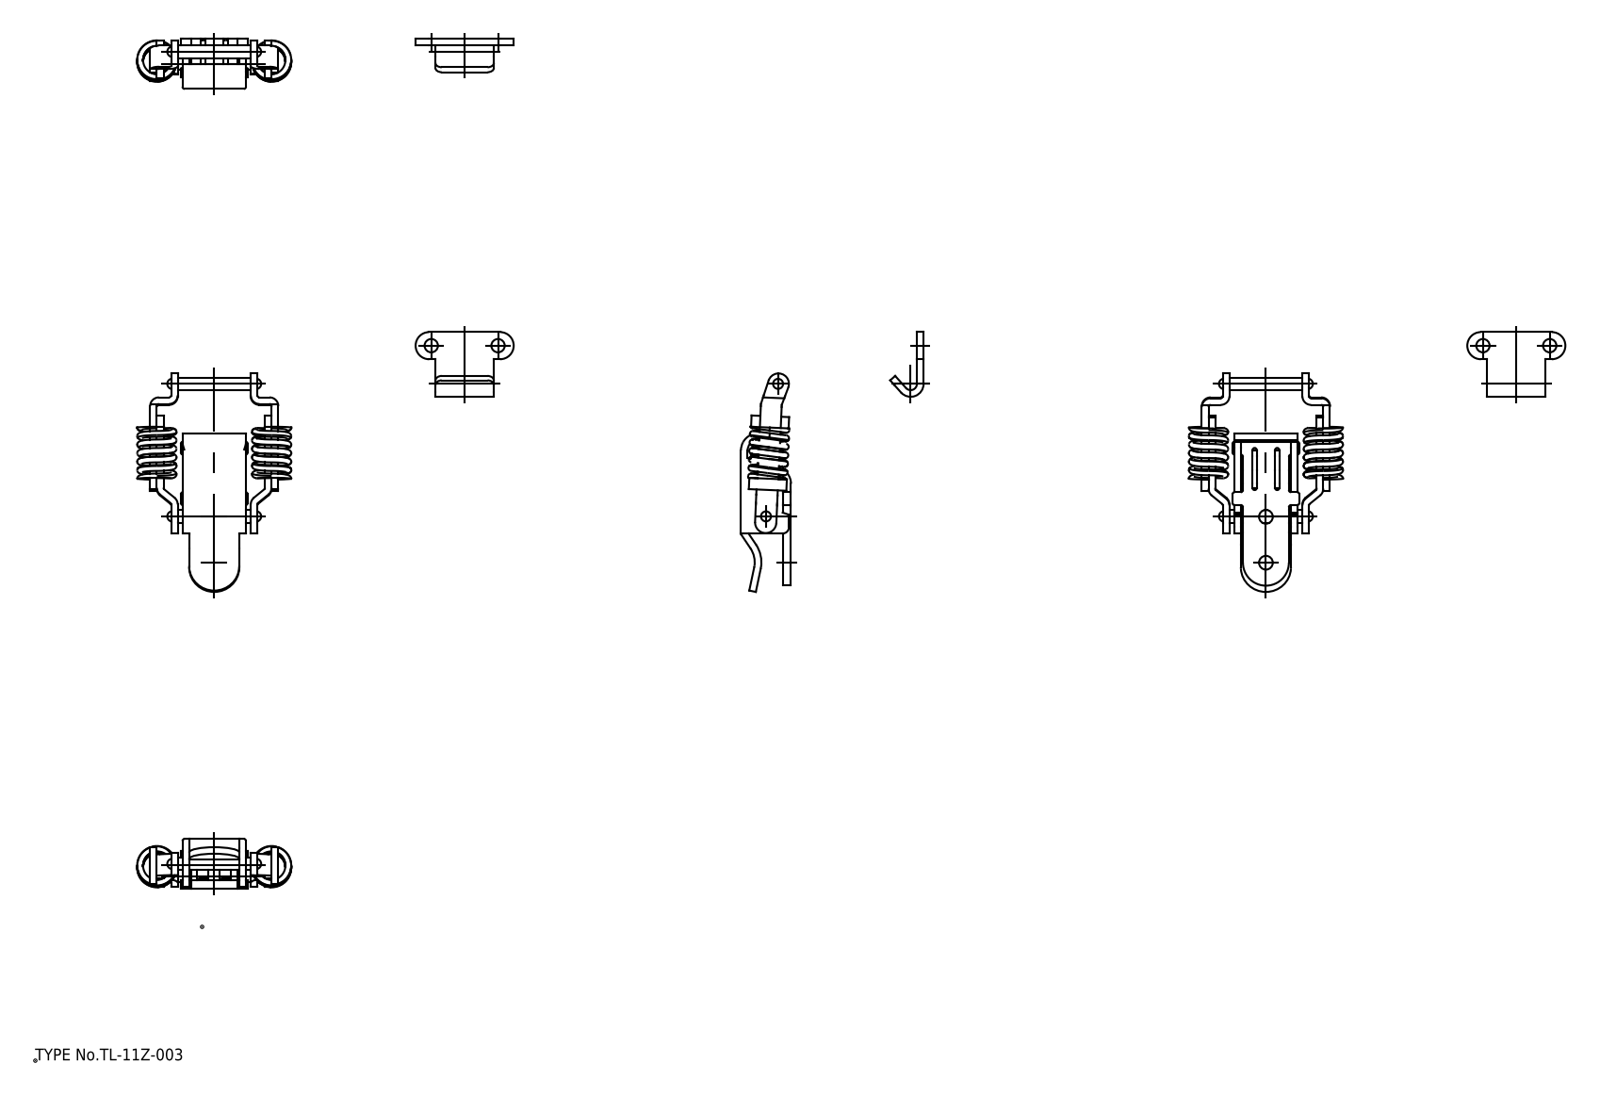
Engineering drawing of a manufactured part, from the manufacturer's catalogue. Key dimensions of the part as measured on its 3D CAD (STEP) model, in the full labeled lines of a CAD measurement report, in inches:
Part name (STEP PRODUCT): arm_AB; arm_C; base; lever (+3 more)
STEP written by: spGate 18.9.1 (****-****-****-****) (AUTOMOTIVE_DESIGN)
Units: inches
Bodies: 7 solids, 389 faces (140 planar, 113 cylindrical, 136 other)
Overall size (bounding box): 2.451 × 1.453 × 0.472
Volume: 0.282 in³ · Surface area: 11.73 in²
Round holes (diameter × count): ⌀0.126 ×3, ⌀0.13 ×2
Round bosses / shafts (diameter × count): ⌀0.118 ×2
Partial cylindrical surfaces — rounded edges, fillets, slot ends (radius × count): R0.02 ×45, R0.083 ×8, R0.059 ×5, R0.079 ×3, R0.098 ×3, R0.128 ×2, R0.142 ×2, R0.161 ×2
Main face-to-face distances: 0.063, 0.841, 0.242, 0.305, 0.778, 0.472, 0.409, 0.079, 1.083, 0.535
Hole centre spacings: 1.644, 2.071, 0.433, 0.63
